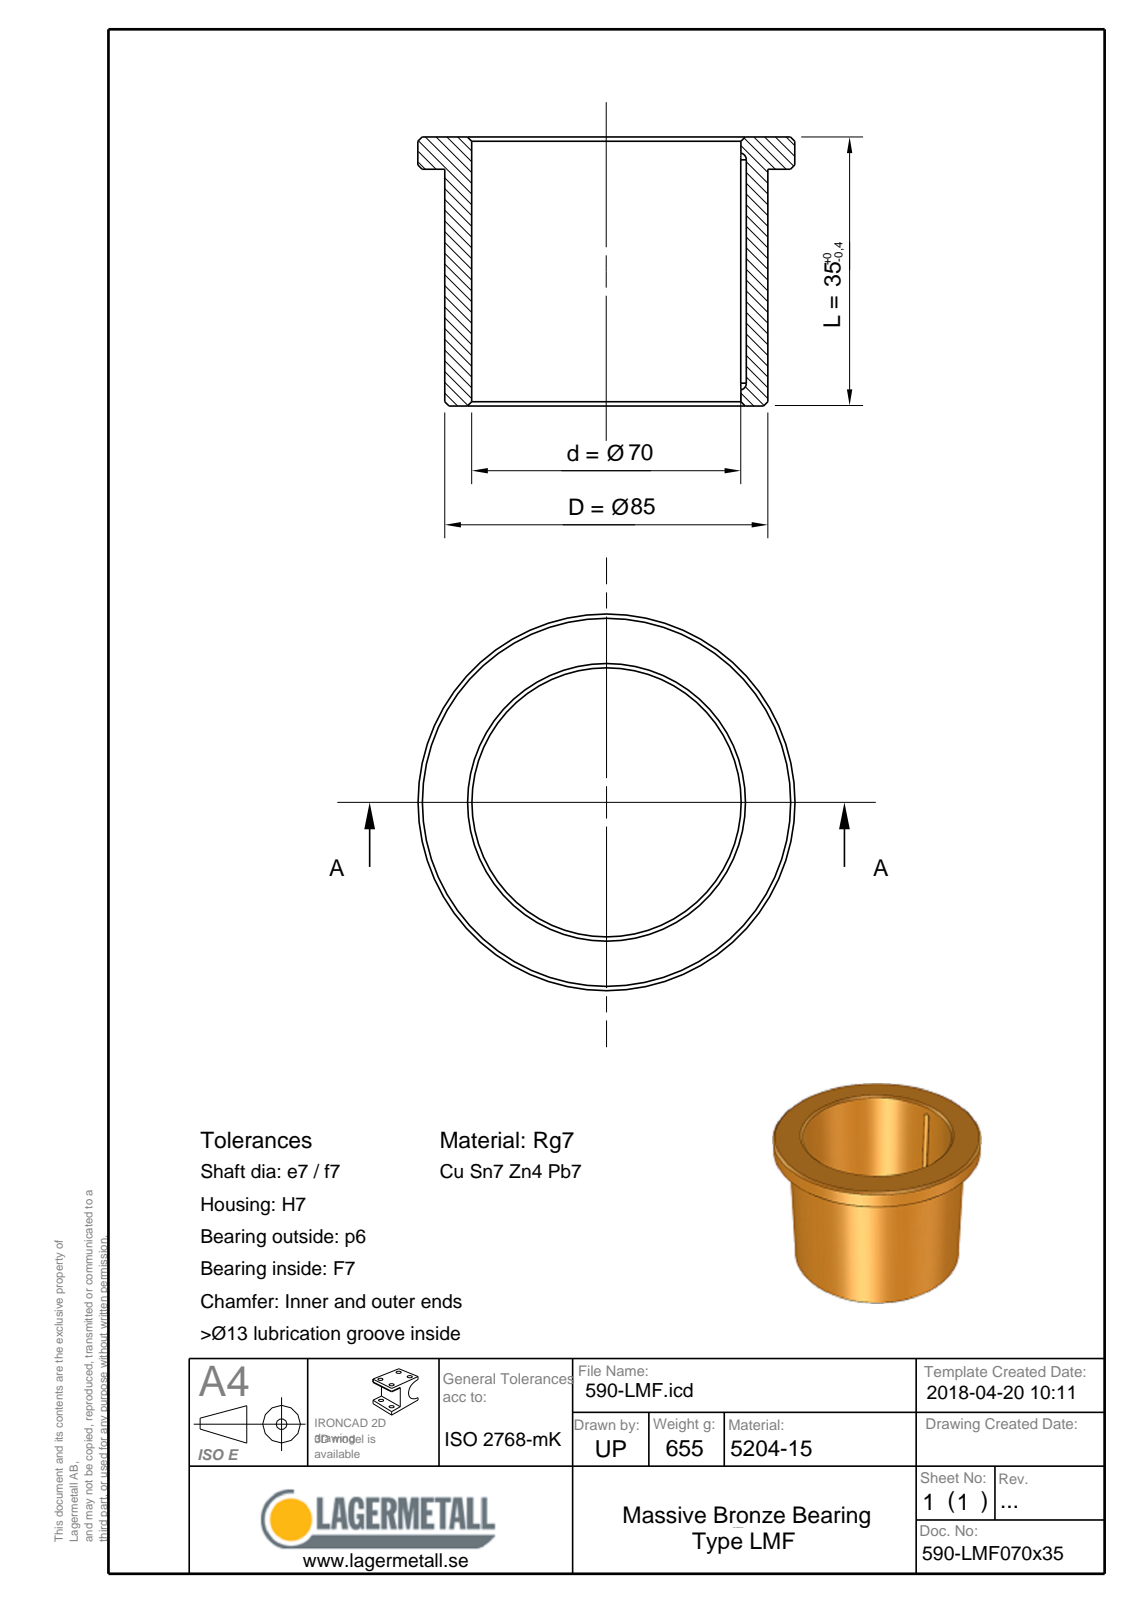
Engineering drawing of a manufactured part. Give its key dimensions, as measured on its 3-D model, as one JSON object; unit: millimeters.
{"part_name": "590-LMF070x35", "step_written_by": "Spatial InterOp 3D (CONFIG_CONTROL_DESIGN)", "units": "millimeters", "bodies": {"solids": 1, "faces": 16, "planar": 4, "cylindrical": 5, "other": 7}, "overall_size": [95, 95, 35], "volume_mm3": 74467, "surface_area_mm2": 23054, "round_holes": [[70, 1]], "round_bosses_or_shafts": [[95, 1], [85, 1]], "partial_cylinders_radius": [[1.75, 2]], "face_to_face_distances": [35, 27, 8]}
